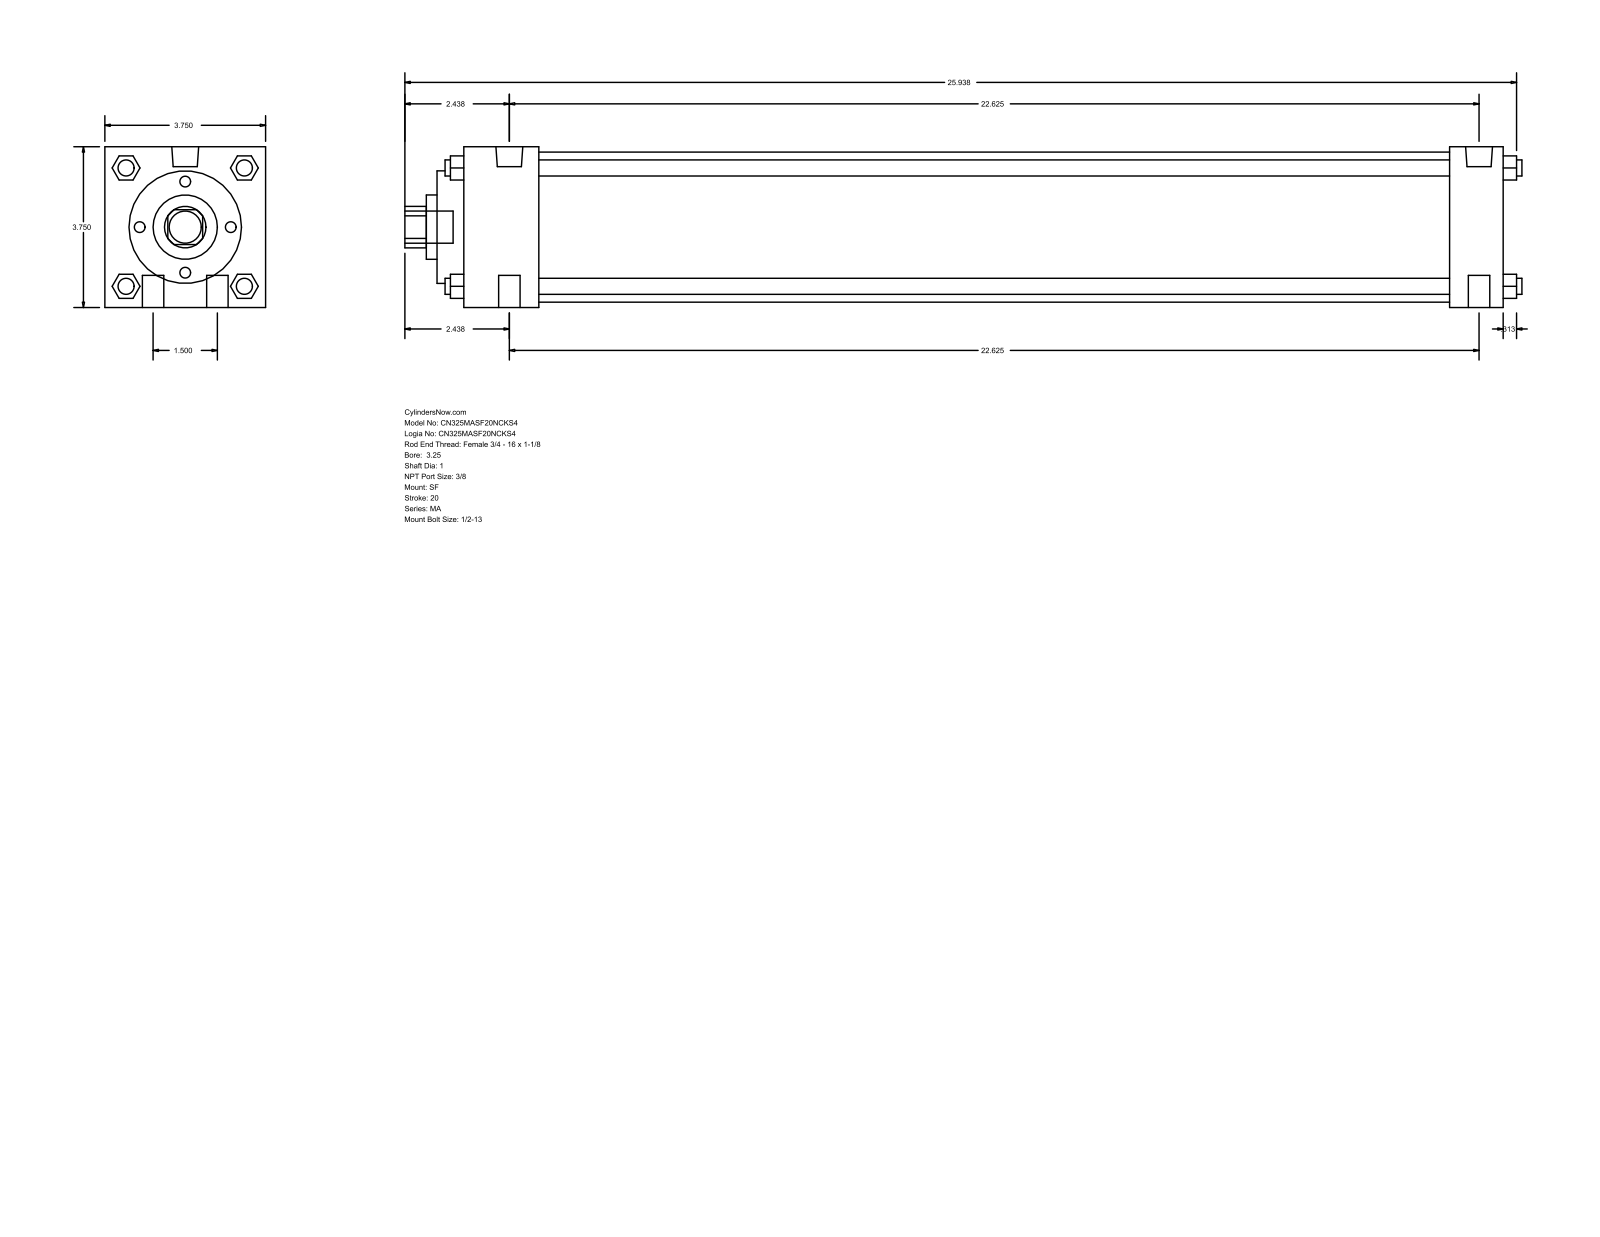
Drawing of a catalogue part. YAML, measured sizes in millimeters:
part_name: "MA_SF__0325_1"
step_written_by: "GSSL Pune (CONFIG_CONTROL_DESIGN)"
units: millimeters
bodies: {solids: 0, faces: 126, planar: 95, cylindrical: 31, other: 0}
overall_size: [661.99, 95.25, 95.25]
round_holes:
  - {diameter: 25.4, count: 1}
  - {diameter: 38.1, count: 1}
  - {diameter: 66.67, count: 1}
  - {diameter: 88.9, count: 1}
round_bosses_or_shafts:
  - {diameter: 12.7, count: 4}
  - {diameter: 9.53, count: 4}
  - {diameter: 15.93, count: 2}
  - {diameter: 11.11, count: 2}
  - {diameter: 19.05, count: 1}
partial_cylinders:
  - {radius: 12.29, count: 1}
face_to_face_distances: [95.24, 615.96, 15.87, 584.2, 31.76, 44.46, 539.74, 571.5, 60.33, 600.07]
